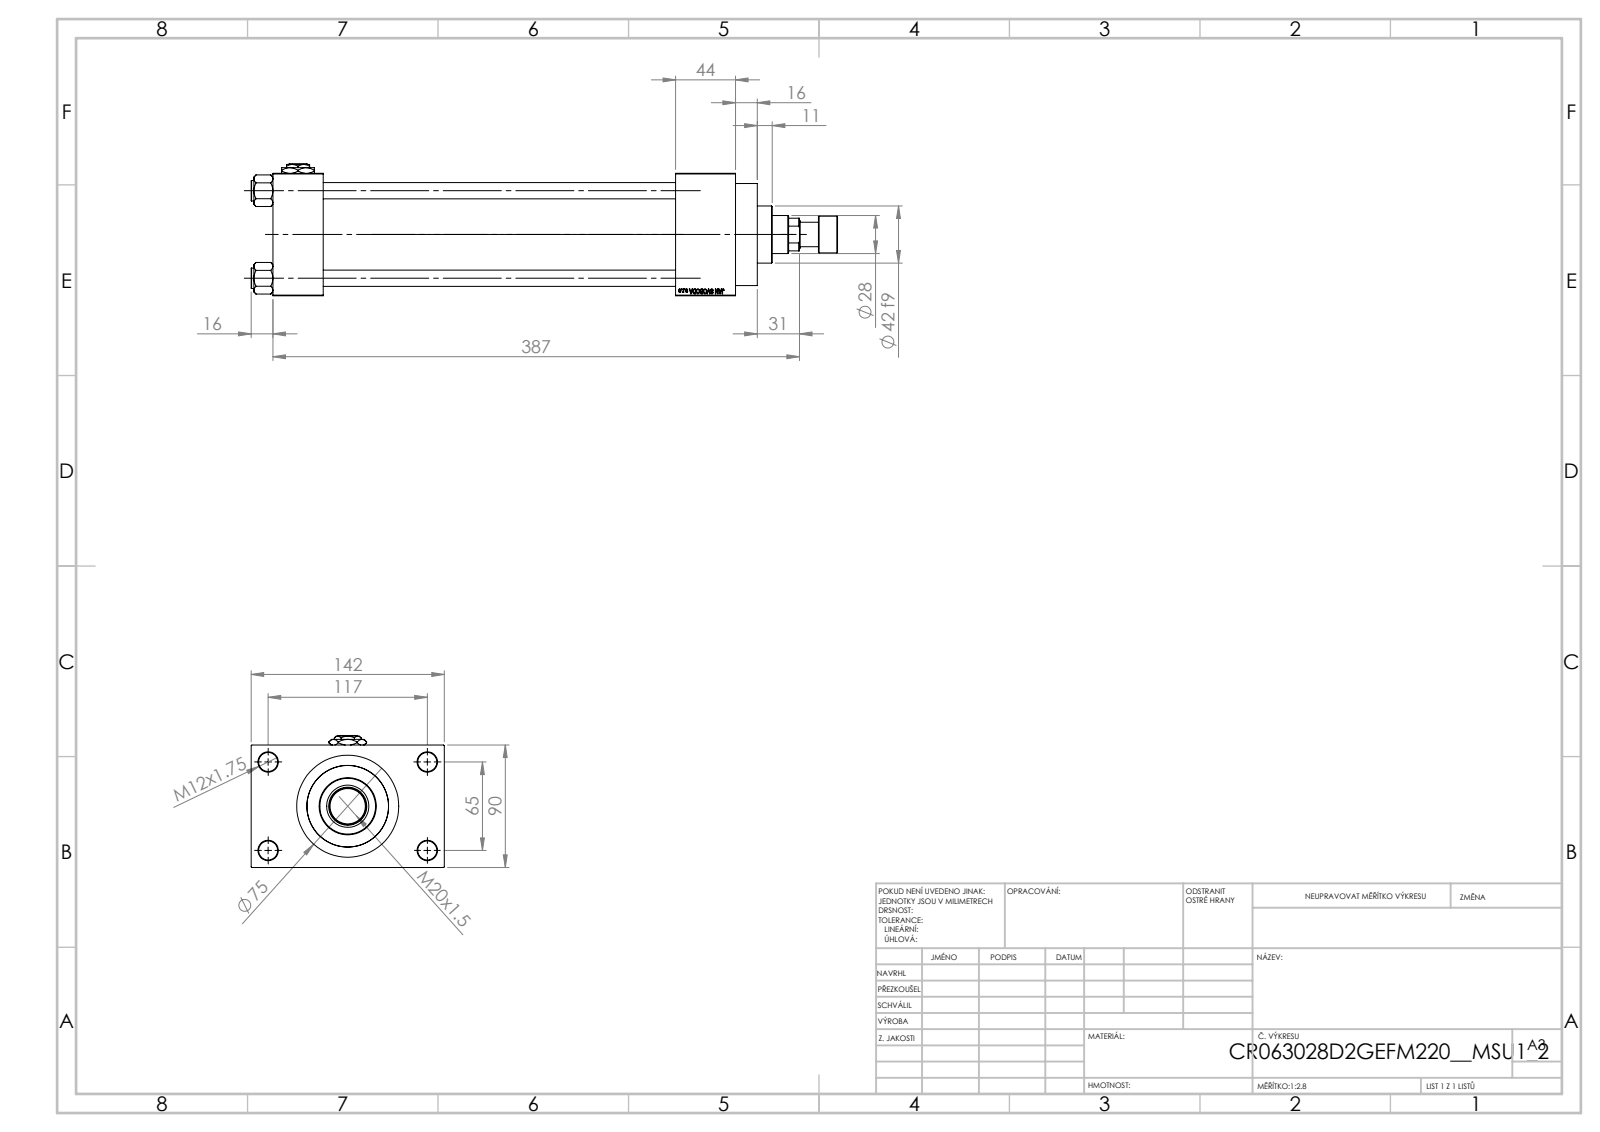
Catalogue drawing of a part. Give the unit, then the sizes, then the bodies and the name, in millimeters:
Units: millimetres
Overall size (bounding box): 431 × 142 × 97
Round holes (diameter × count): ⌀12 ×4, ⌀14 ×4, ⌀7 ×2, ⌀20.96 ×2, ⌀30 ×2, ⌀18.5 ×1, ⌀28 ×1, ⌀31 ×1, ⌀50 ×1, ⌀60 ×1, ⌀63 ×1
Round bosses / shafts (diameter × count): ⌀15 ×4, ⌀75 ×1, ⌀69 ×1, ⌀42 ×1, ⌀27 ×1, ⌀18 ×1
Main face-to-face distances: 90, 259, 37, 296, 303, 340, 44, 26, 116, 142
Hole centre spacings: 26.35, 45.47, 64.3, 66.92, 69.81, 90.65, 111.34, 65
Volume: 1 452 000 mm³ · Surface area: 335 327 mm²
Bodies: 13 solids, 1171 faces (525 planar, 100 cylindrical, 546 other)
Part name (STEP PRODUCT): V215CR_D_TYCINKA; V215CR_ROD_END_F; V215_VC_A; NUT_M5_D (+3 more)
STEP written by: SolidWorks 2019 (CONFIG_CONTROL_DESIGN)
